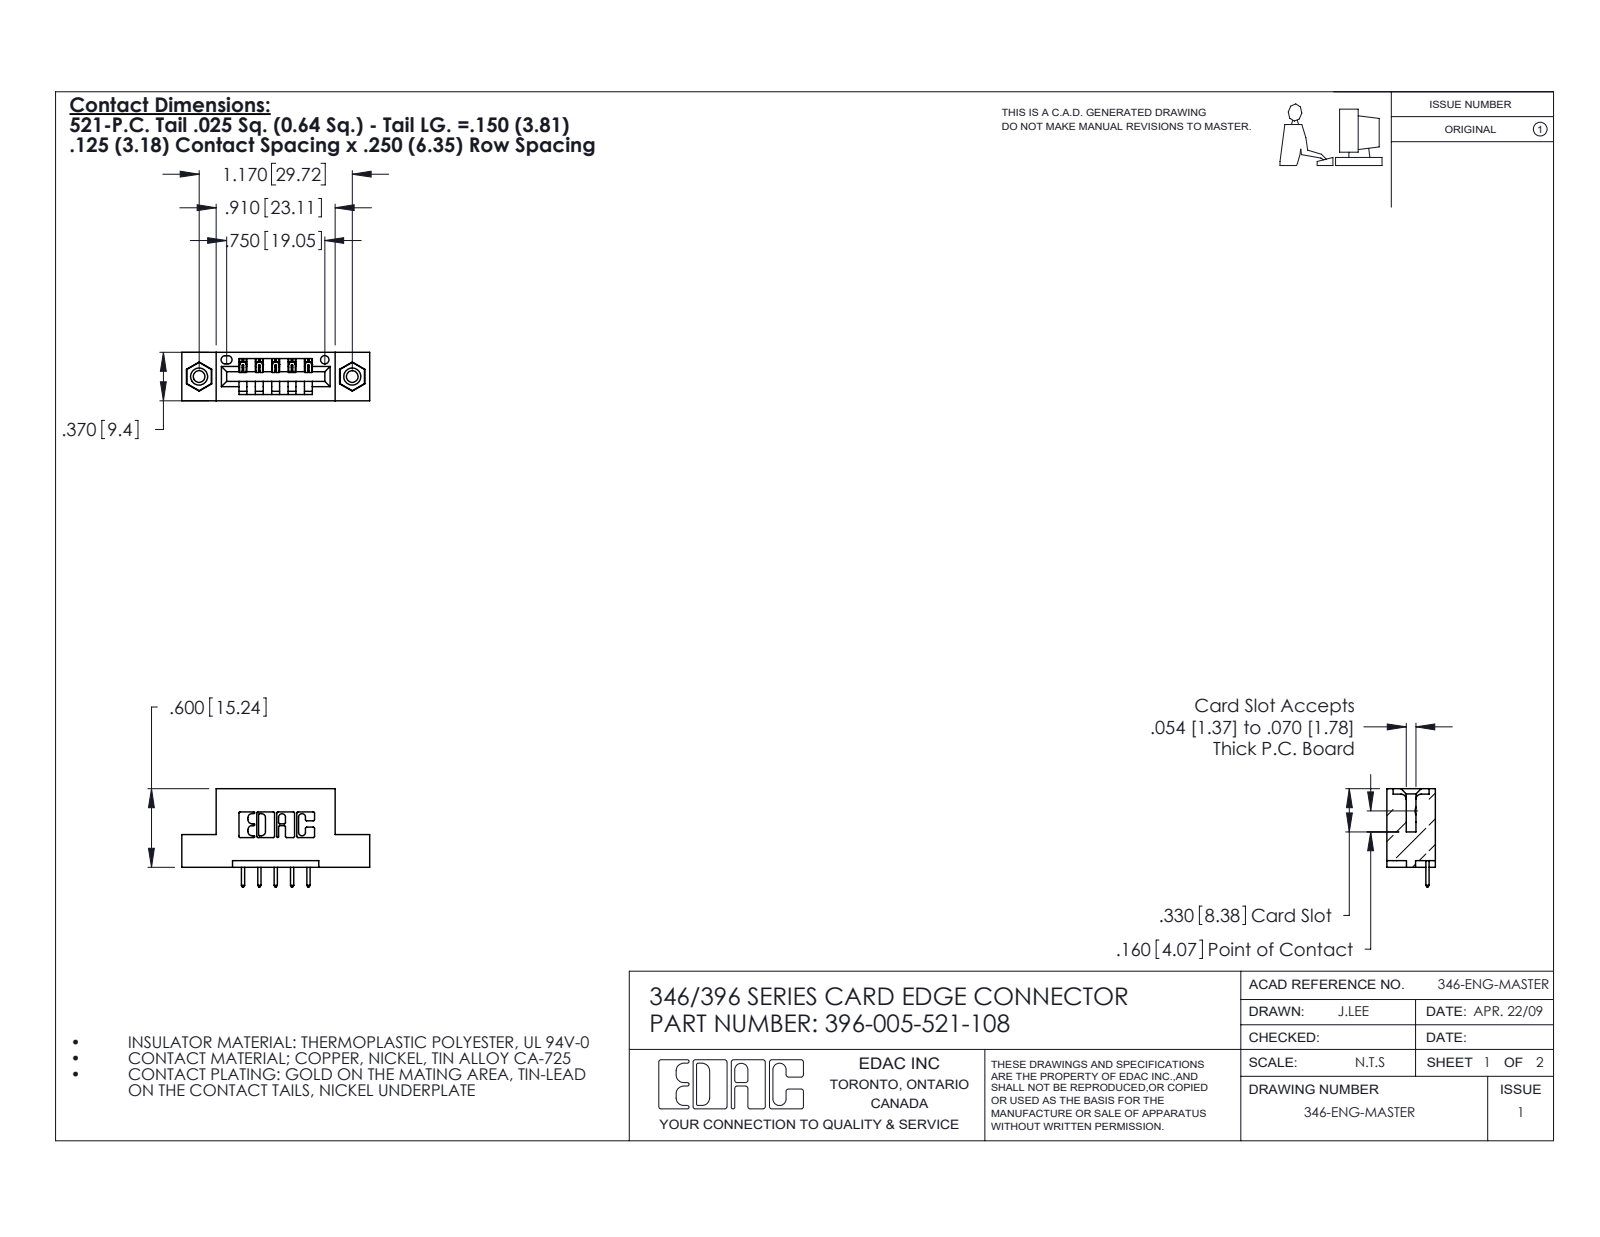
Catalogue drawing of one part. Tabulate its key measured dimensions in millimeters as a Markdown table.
| quantity | value |
| --- | --- |
| part name | 396-005-521-108; 345-250-001_345-250-003-102; 346 Part_Flush Mounting Lugs - 0.156 Dia-TI; 345-292-001_345-293-121 |
| STEP written by | SolidWorks 2020 (CONFIG_CONTROL_DESIGN) |
| units | millimeters |
| bodies | 8 solids, 472 faces (308 planar, 148 cylindrical, 16 other) |
| overall size | 36.4 × 19.1 × 9.4 |
| volume | 3 210 mm³ |
| surface area | 3 582 mm² |
| round holes (diameter × count) | 2.3 × 2, 3.2 × 2, 4 × 2, 1.6 × 1 |
| round bosses / shafts (diameter × count) | 3.9 × 2 |
| partial cylindrical surfaces (radius × count) | 0.3 × 22, 0.2 × 10, 0.3 × 10, 0.2 × 6, 0.8 × 6, 0.7 × 3, 0.8 × 2, 1 × 2 |
| main face-to-face distances | 6.4, 9.4, 1.2, 8.2, 14, 3.8, 5.6, 2.5, 4.4, 3.2 |
| hole center spacings | 6.2, 24.6, 29.7 |
